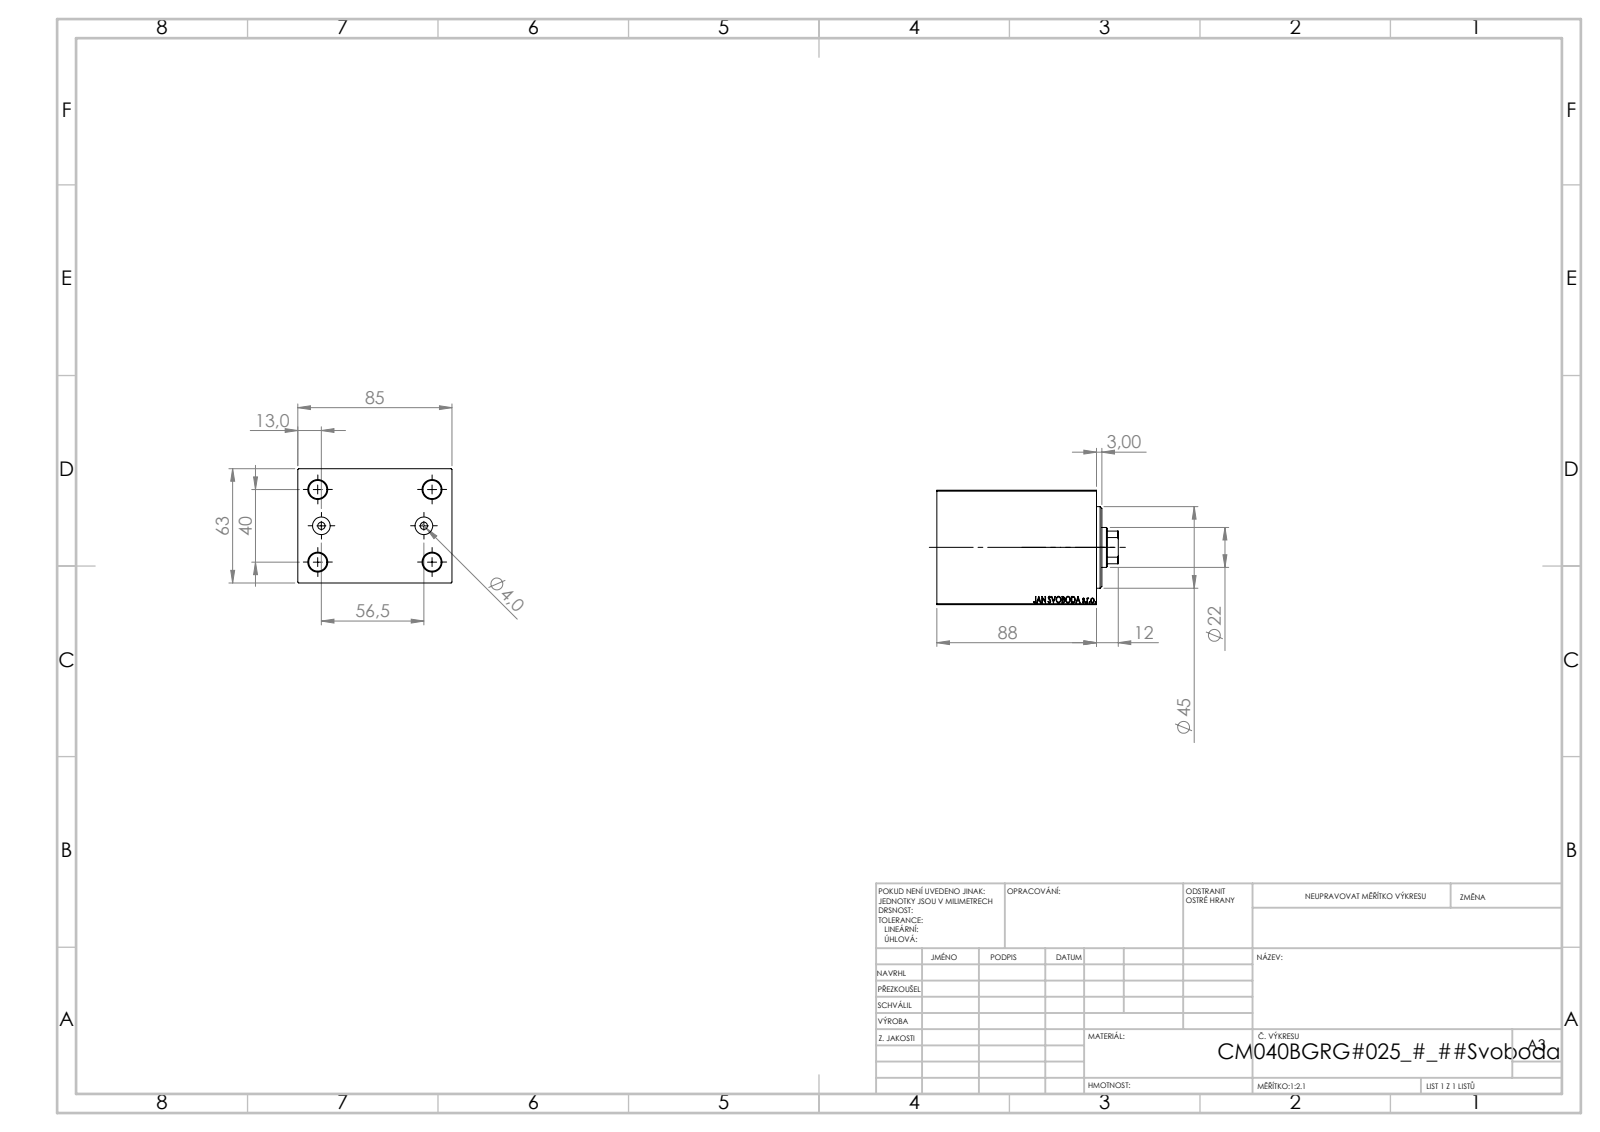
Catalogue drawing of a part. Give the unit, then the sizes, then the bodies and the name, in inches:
Units: inches
Overall size (bounding box): 3.937 × 3.346 × 2.48
Round holes (diameter × count): ⌀0.394 ×4, ⌀0.157 ×2, ⌀0.383 ×2, ⌀0.492 ×1, ⌀0.866 ×1, ⌀1.004 ×1, ⌀1.043 ×1, ⌀1.575 ×1, ⌀1.654 ×1, ⌀1.772 ×1
Partial cylindrical surfaces — rounded edges, fillets, slot ends (radius × count): R0.413 ×1
Main face-to-face distances: 2.48, 3.346, 0.472, 2.992, 3.465, 2.52, 0.118, 0.591, 3.11, 3.583
Hole centre spacings: 1.469, 0.791, 0.807, 1.575, 2.434, 2.48, 2.528, 2.938
Volume: 26.7 in³ · Surface area: 109.8 in²
Bodies: 3 solids, 877 faces (401 planar, 50 cylindrical, 426 other)
Part name (STEP PRODUCT): V450CM_B_VCP; V450CM_VC_B; V450CM_B_Body
STEP written by: SolidWorks 2019 (CONFIG_CONTROL_DESIGN)
